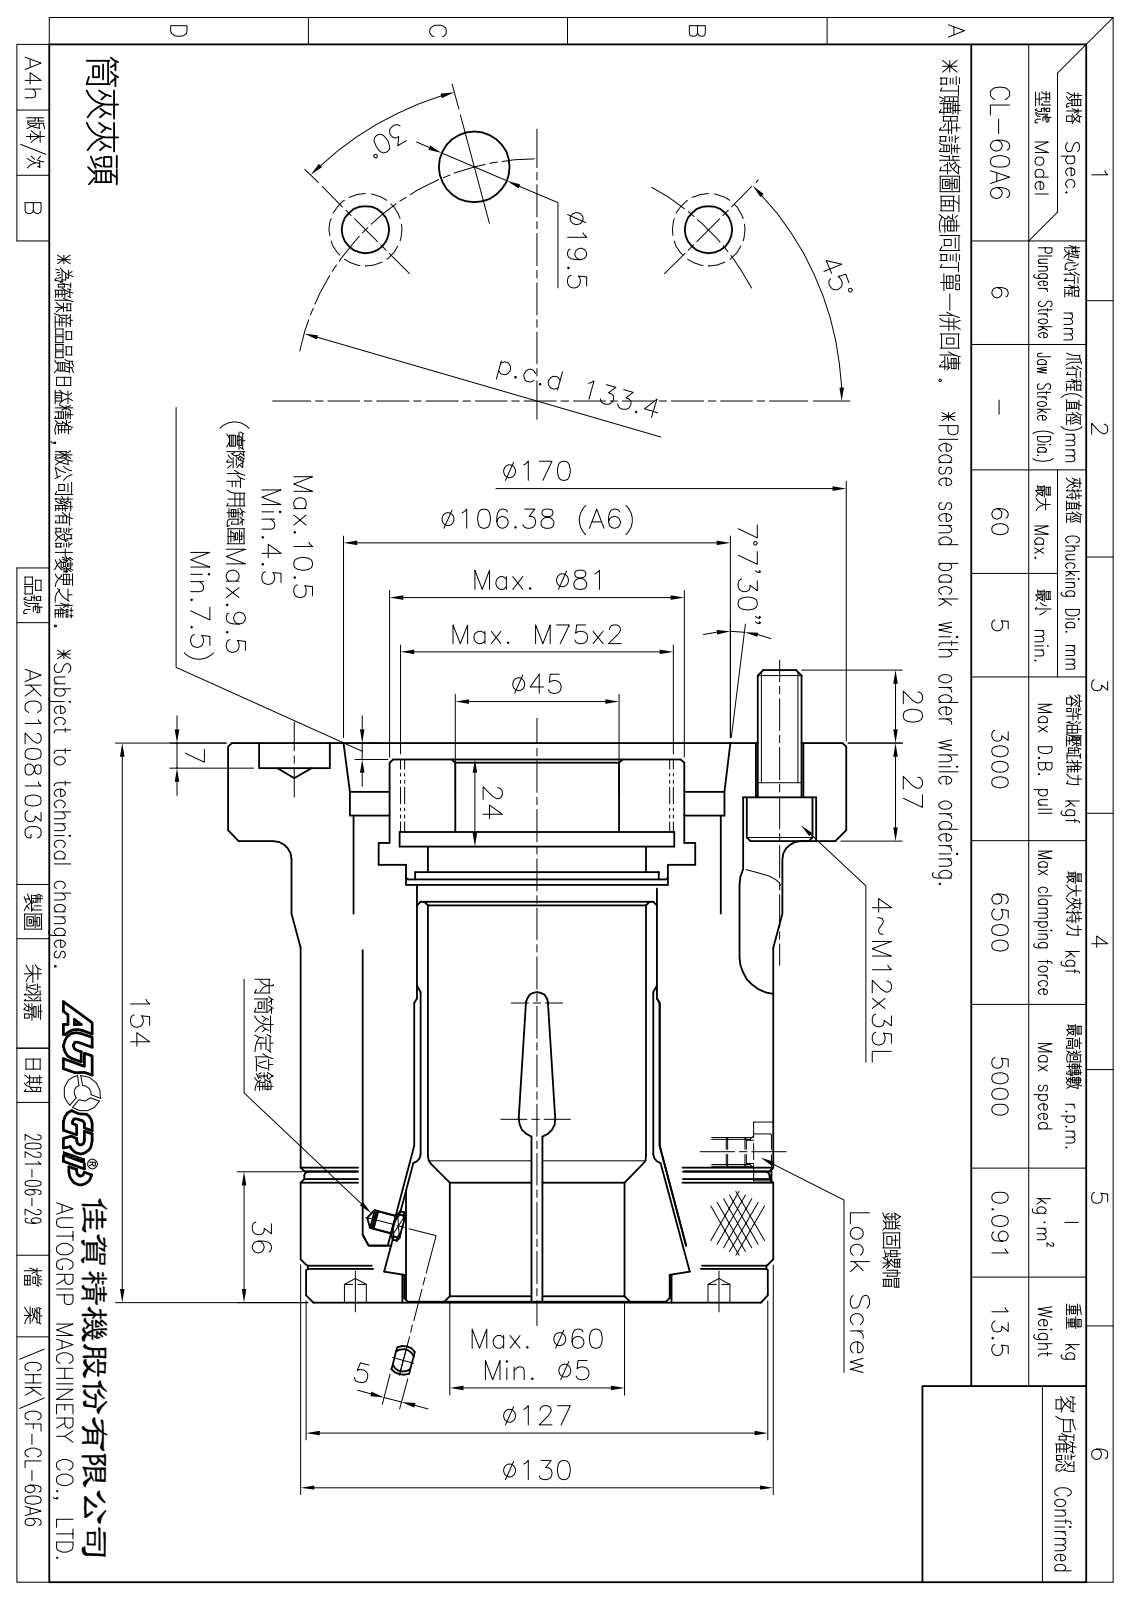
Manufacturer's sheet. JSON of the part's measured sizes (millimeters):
{"part_name": "CF-CL-60A6; 圓頭內六角螺栓_M12x35; CF-CL-42-08000; CF-FSW320300 (+4 more)", "step_written_by": "SolidWorks 2016 (CONFIG_CONTROL_DESIGN)", "units": "millimeters", "bodies": {"solids": 10, "faces": 383, "planar": 117, "cylindrical": 120, "other": 146}, "overall_size": [174, 170, 170], "volume_mm3": 1581000, "surface_area_mm2": 284893, "round_holes": [[13.5, 4], [20, 4], [6, 2], [19.5, 2], [5, 1], [6.8, 1], [60, 1], [66, 1], [67, 1], [67.5, 1], [72, 1], [73, 1]], "round_bosses_or_shafts": [[18, 4], [12, 4], [170, 1], [135, 1], [130, 1], [128, 1], [127, 1], [126, 1]], "partial_cylinders_radius": [[10, 4], [8.5, 3], [4, 1], [8, 1], [8.25, 1]], "face_to_face_distances": [154, 6.5, 27, 127, 33.5, 120.5, 12, 117.8, 96.3, 21.5], "hole_center_spacings": [66.69, 94.32, 22.49, 34.53, 50, 66.7, 72.26, 72.27]}
